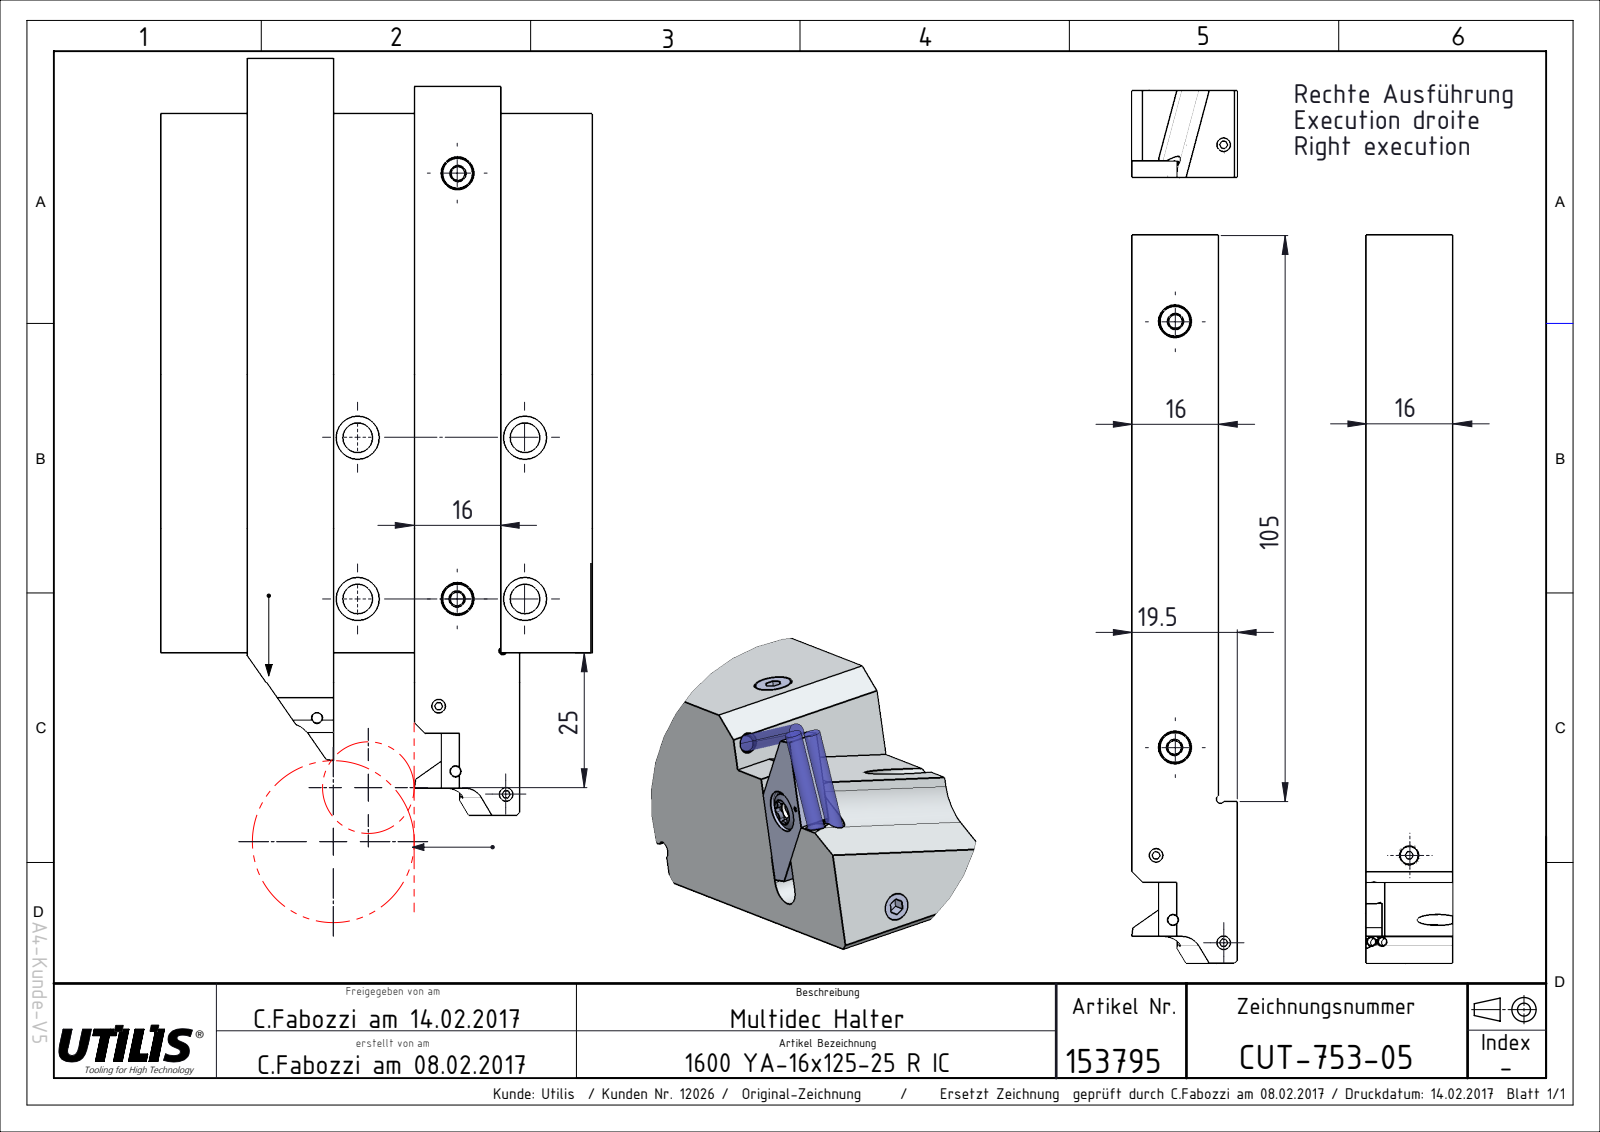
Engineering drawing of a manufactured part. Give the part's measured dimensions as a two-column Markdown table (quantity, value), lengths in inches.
| quantity | value |
| --- | --- |
| part name | CUT-753_Platte_10006; CUT-753-05; CUT-753_Kunde_05 |
| STEP written by | SolidWorks 2016 (CONFIG_CONTROL_DESIGN) |
| units | inches |
| bodies | 2 solids, 73 faces (45 planar, 14 cylindrical, 14 other) |
| overall size | 5.315 × 0.768 × 0.63 |
| volume | 2.095 in³ |
| surface area | 14.68 in² |
| round holes (diameter × count) | 0.071 × 2, 0.114 × 1, 0.122 × 1 |
| partial cylindrical surfaces (radius × count) | 0.02 × 1, 0.03 × 1, 0.061 × 1, 0.067 × 1, 0.138 × 1 |
| main face-to-face distances | 0.63, 0.768, 0.138, 5.315, 0.591, 0.118, 0.512, 4.724, 0.433, 0.197 |
| hole center spacings | 0.078 |
